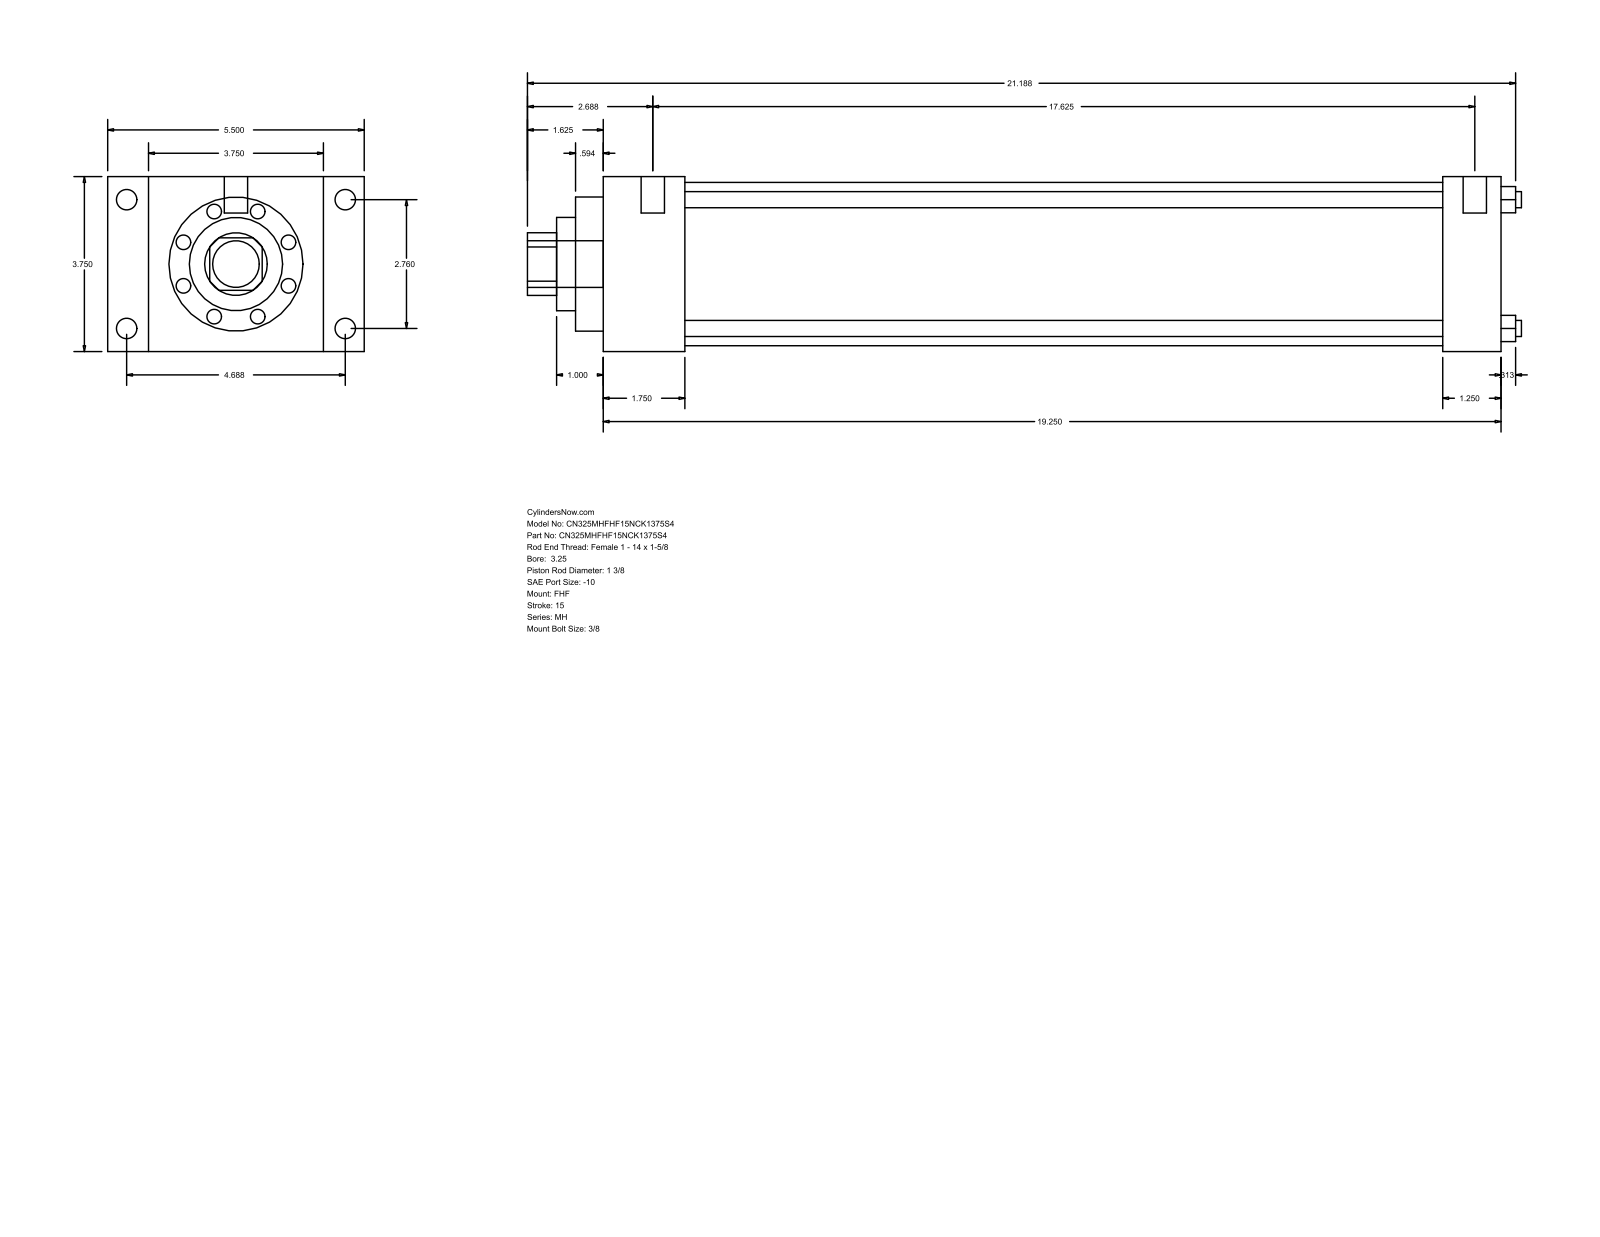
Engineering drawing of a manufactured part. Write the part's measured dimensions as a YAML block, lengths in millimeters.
part_name: "MH_FHF__0325_1.375"
step_written_by: "GSSL Pune (CONFIG_CONTROL_DESIGN)"
units: millimeters
bodies: {solids: 0, faces: 90, planar: 61, cylindrical: 29, other: 0}
overall_size: [541.34, 139.7, 95.25]
round_holes:
  - {diameter: 8.76, count: 4}
  - {diameter: 34.92, count: 1}
  - {diameter: 50.8, count: 1}
  - {diameter: 73.03, count: 1}
  - {diameter: 88.9, count: 1}
round_bosses_or_shafts:
  - {diameter: 11.13, count: 4}
  - {diameter: 5.56, count: 4}
  - {diameter: 12.7, count: 2}
  - {diameter: 25.4, count: 1}
partial_cylinders:
  - {radius: 17.06, count: 1}
face_to_face_distances: [95.24, 488.96, 44.45, 444.51, 22.23, 117.47, 139.7, 457.21, 412.76, 31.75]
hole_center_spacings: [49.57, 70.1, 99.14]
